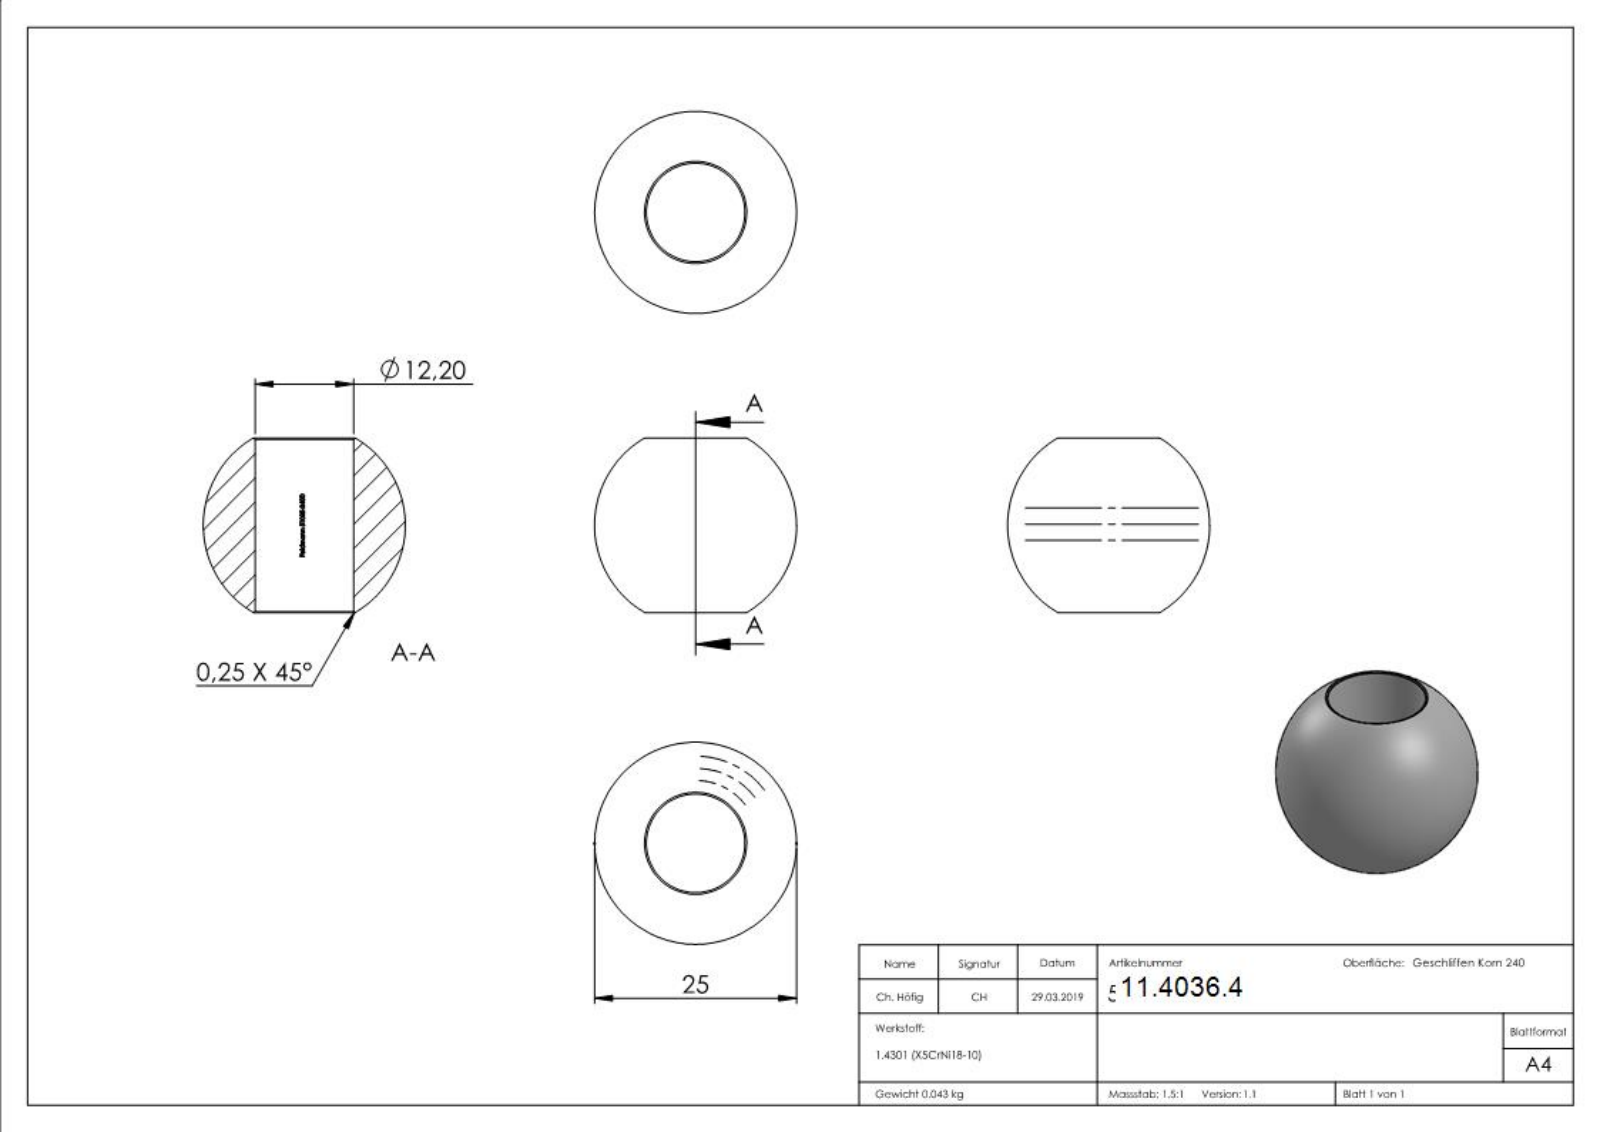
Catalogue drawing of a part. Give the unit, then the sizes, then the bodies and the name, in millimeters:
Units: millimetres
Overall size (bounding box): 25 × 25 × 21.57
Round holes (diameter × count): ⌀12.2 ×1
Partial cylindrical surfaces — rounded edges, fillets, slot ends (radius × count): R6.2 ×1
Main face-to-face distances: 2.98, 1.19, 5.85, 0.66, 1.74, 0.61, 0.55, 0.53, 0.35, 3.48
Volume: 5 438 mm³ · Surface area: 2 535 mm²
Bodies: 1 solid, 241 faces (107 planar, 27 cylindrical, 107 other)
Part name (STEP PRODUCT): 51025-240D
STEP written by: SolidWorks 2015 (CONFIG_CONTROL_DESIGN)
